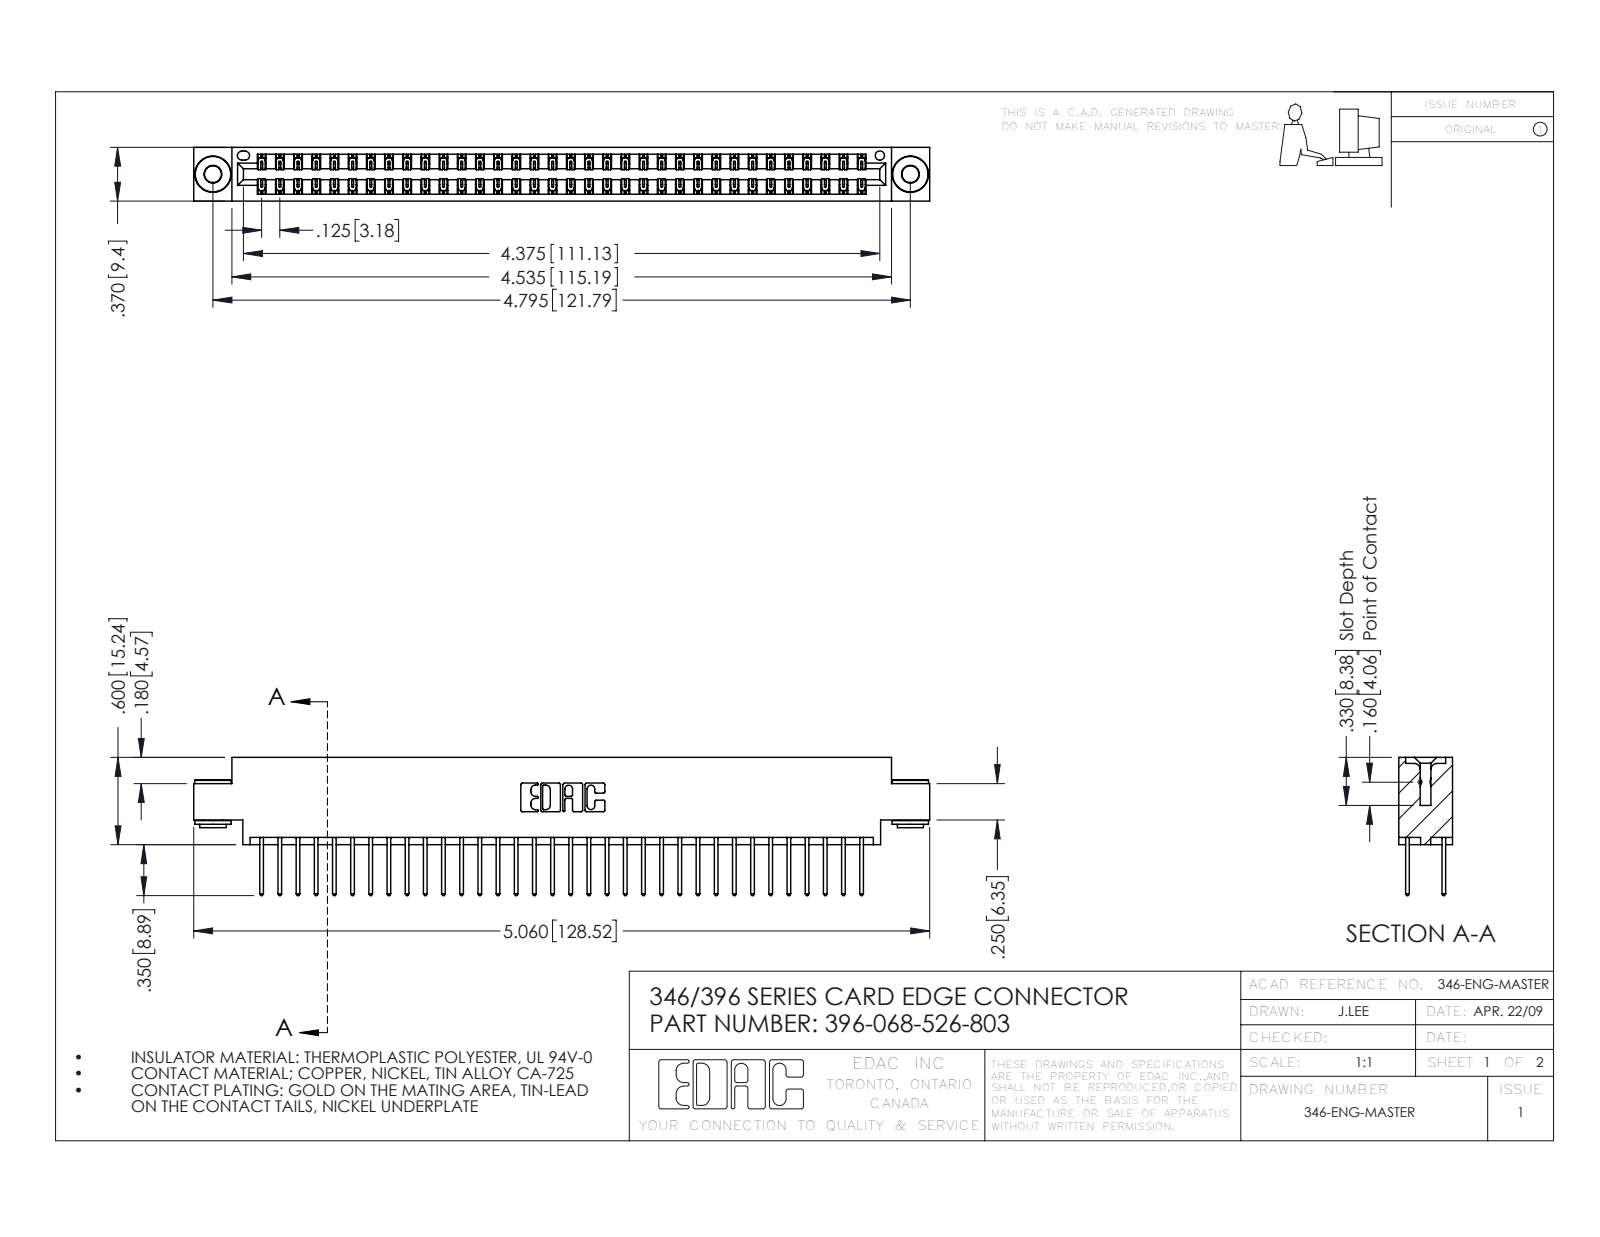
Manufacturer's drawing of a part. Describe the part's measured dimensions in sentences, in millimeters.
The part is named "346 Part_0.170 Offset - 0.156 Dia-TH; 345-250-002_345-250-002-102; 396-068-526-803; 345-292-001_345-293-126". Its 3-D file was written by "SolidWorks 2016 (CONFIG_CONTROL_DESIGN)". It is 71 solids with 3700 faces: 2470 planar, 1222 cylindrical and 8 other. Overall it measures 128.5 by 24.1 by 9.4 millimeters. Its volume is 12 500 cubic millimeters and its surface area 17 880 square millimeters. Round holes: 2 of diameter 2.9, 2 of diameter 4, 1 of diameter 1.6. Round bosses or shafts: 2 of diameter 6.4, 2 of diameter 4.6, 2 of diameter 3.5. Partial cylindrical surfaces (rounded edges, fillets, slot ends): 102 of radius 0.2, 68 of radius 0.3, 22 of radius 0.3, 6 of radius 0.2, 6 of radius 0.8, 3 of radius 0.7, 2 of radius 0.4, 2 of radius 0.6. The main face-to-face distances are 1.2, 8.2, 6.4, 9.4, 0.6, 1.8, 7.6, 7, 3.8, 5.6. The hole center spacings are 6.2, 116.5, 121.8.
